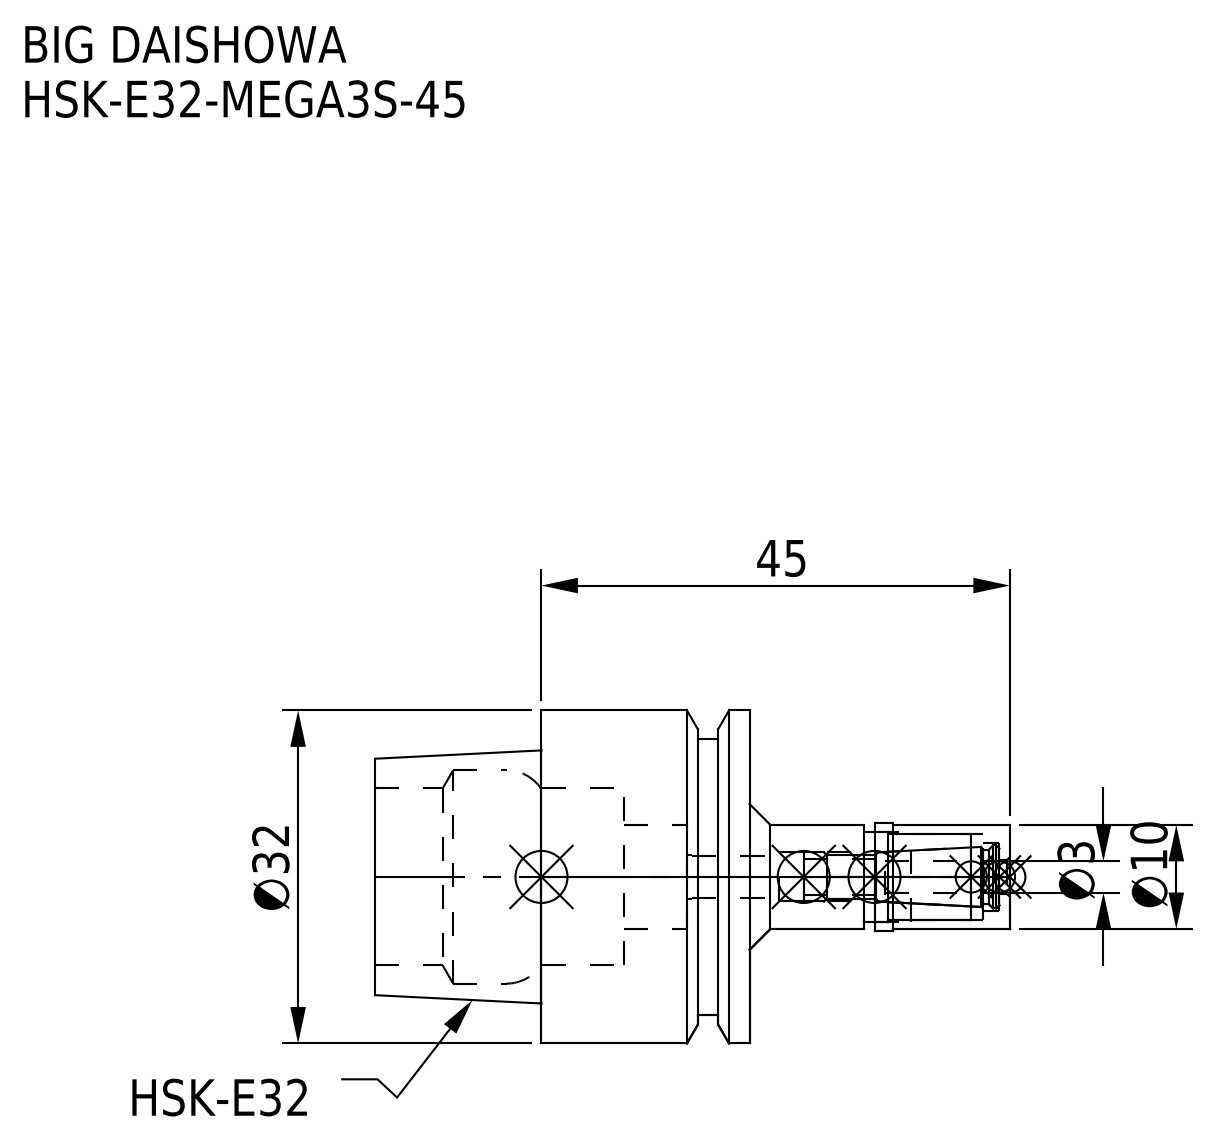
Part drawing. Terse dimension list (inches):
name: HE32MS03045-030_ASM.stp; HSK-E32-MEGA3S-45; HSK-E32-MEGA3S-45-030.stp; DXF_TEMP_ASSY_ASM_4_ASM.stp (+3 more)
written by: SolidWorks 2019 (CONFIG_CONTROL_DESIGN)
unit: in
bodies: 2 solids, 74 faces (18 planar, 40 cylindrical, 16 other)
size: 2.402 × 1.26 × 1.26
volume: 1.041 in³; area: 13.23 in²
holes: 1× ⌀0.13, 1× ⌀0.161, 1× ⌀0.165, 1× ⌀0.185, 1× ⌀0.26, 1× ⌀0.323, 1× ⌀0.343, 1× ⌀0.669, 1× ⌀0.807
bosses: 1× ⌀1.26, 1× ⌀1.043, 1× ⌀0.406, 1× ⌀0.394
face distances: 0.787, 0.63, 1.417, 0.474, 0.313, 0.943, 0.591, 0.669, 1.22, 0.197
